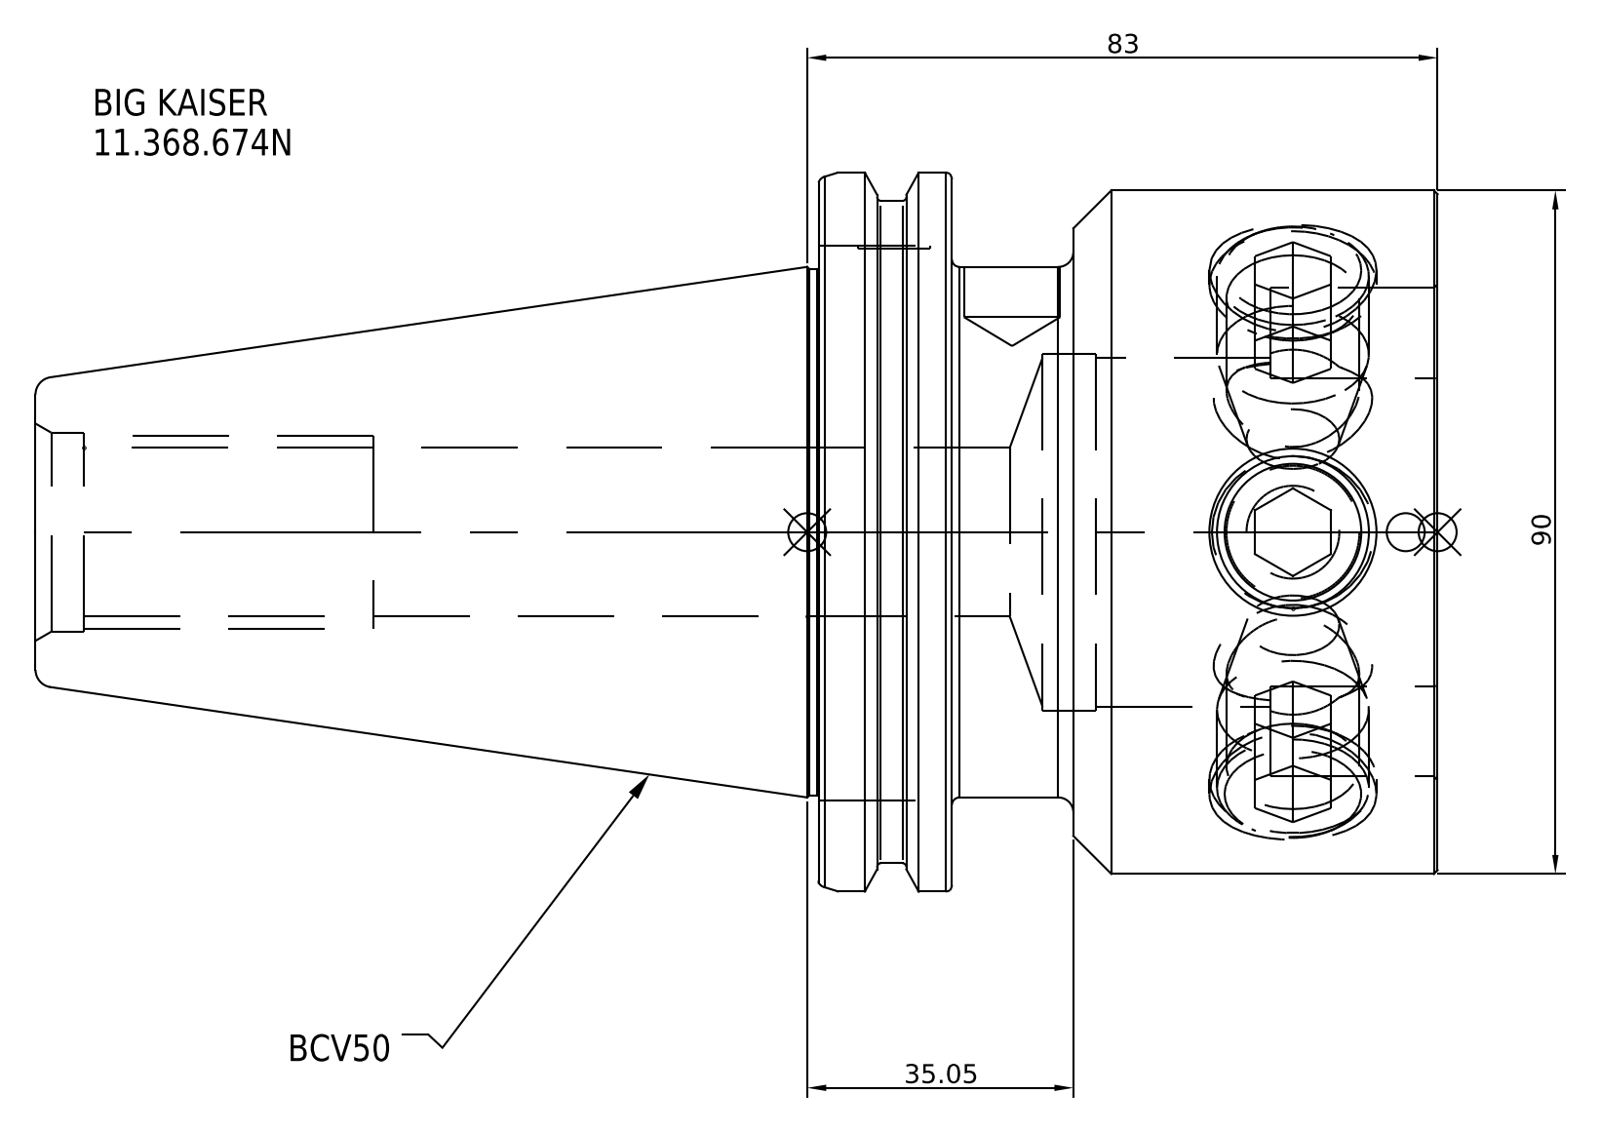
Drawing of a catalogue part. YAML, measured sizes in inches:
part_name: "11.368.674N"
step_written_by: "SolidWorks 2021 (CONFIG_CONTROL_DESIGN)"
units: inches
bodies: {solids: 1, faces: 16, planar: 7, cylindrical: 6, other: 3}
overall_size: [7.268, 3.875, 3.875]
volume: 45.64
surface_area: 92.39
round_bosses_or_shafts:
  - {diameter: 3.875, count: 1}
  - {diameter: 3.594, count: 1}
  - {diameter: 3.543, count: 1}
  - {diameter: 2.75, count: 1}
face_to_face_distances: [3.209, 2.518, 0.691, 1.89, 0.628, 1.319, 7.268, 5.378, 4.75, 4.059]
